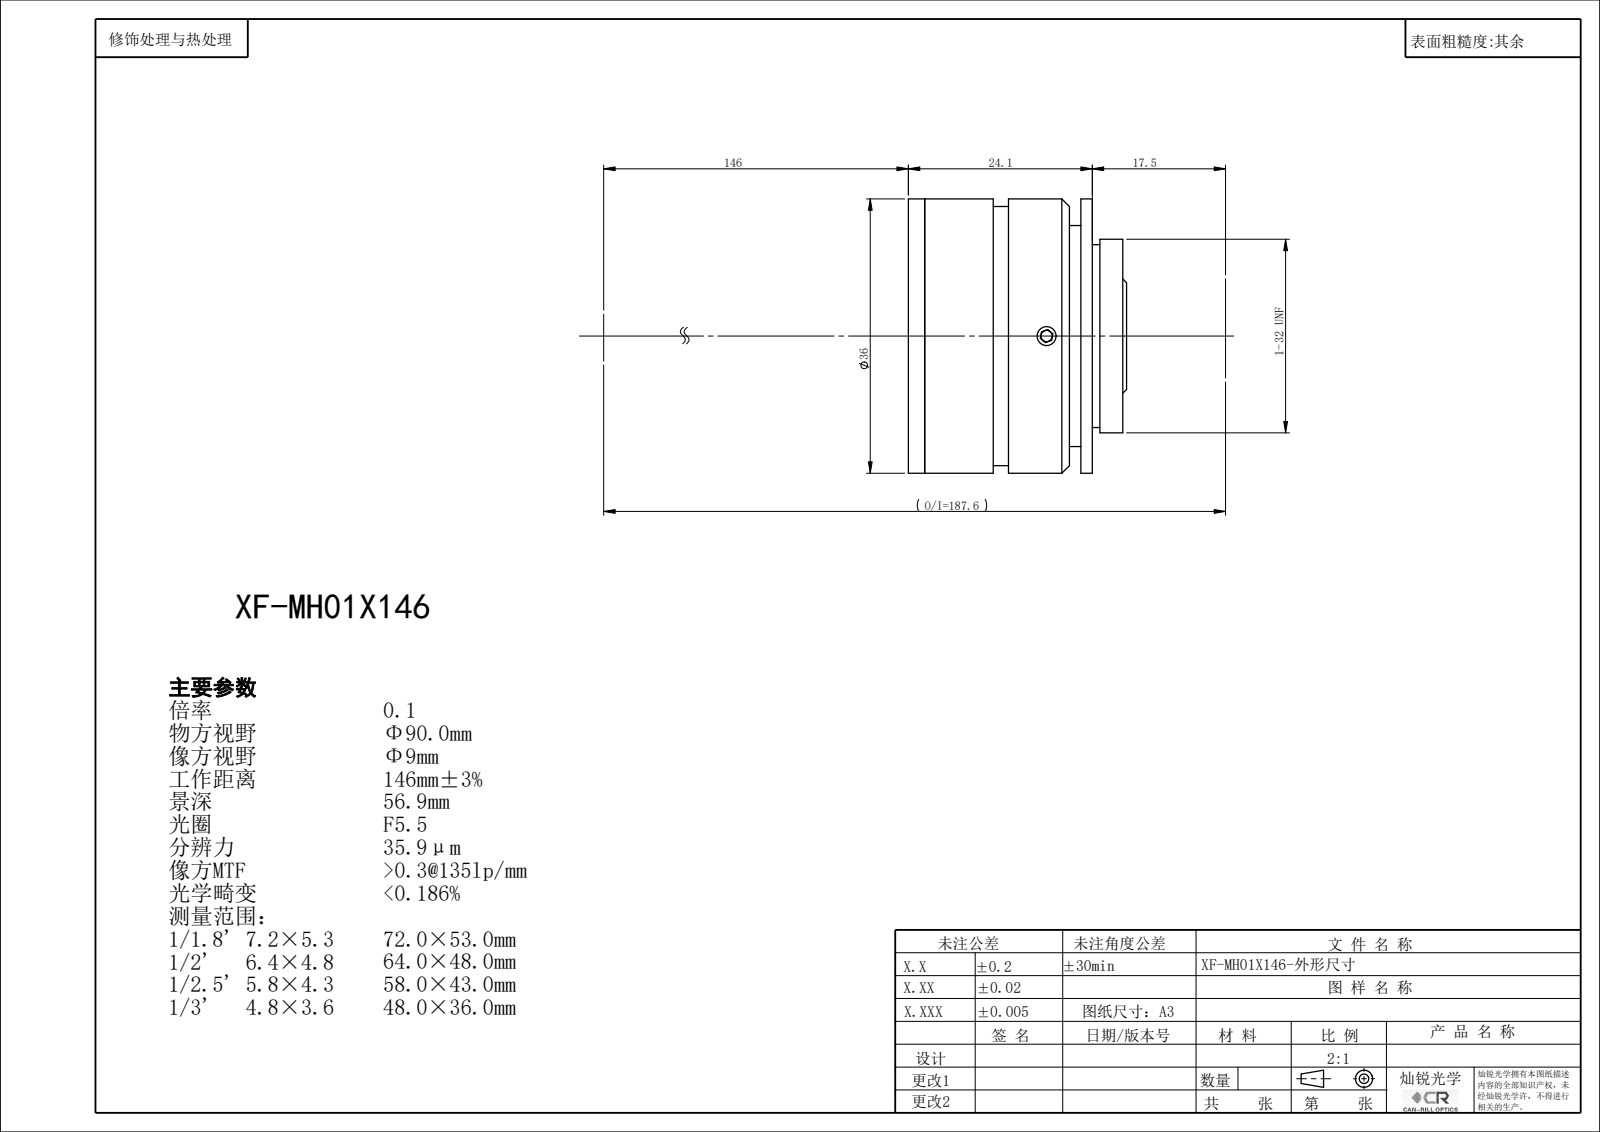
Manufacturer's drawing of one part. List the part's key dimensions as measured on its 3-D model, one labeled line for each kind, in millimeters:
Part name (STEP PRODUCT): XF-MH01X146
STEP written by: SolidWorks 2022 (CONFIG_CONTROL_DESIGN)
Units: millimetres
Bodies: 0 solids, 107 faces (51 planar, 46 cylindrical, 10 other)
Overall size (bounding box): 36 × 36 × 28.65
Round holes (diameter × count): ⌀2.5 ×3, ⌀7 ×1, ⌀8.4 ×1, ⌀10 ×1, ⌀12 ×1, ⌀14 ×1, ⌀16 ×1, ⌀18 ×1, ⌀20 ×1, ⌀21.5 ×1, ⌀22 ×1, ⌀24 ×1
Round bosses / shafts (diameter × count): ⌀36 ×1, ⌀34 ×1, ⌀25.4 ×1
Main face-to-face distances: 2.15, 1.5, 22, 24.15, 3, 22.65, 2, 1, 20.5, 4
